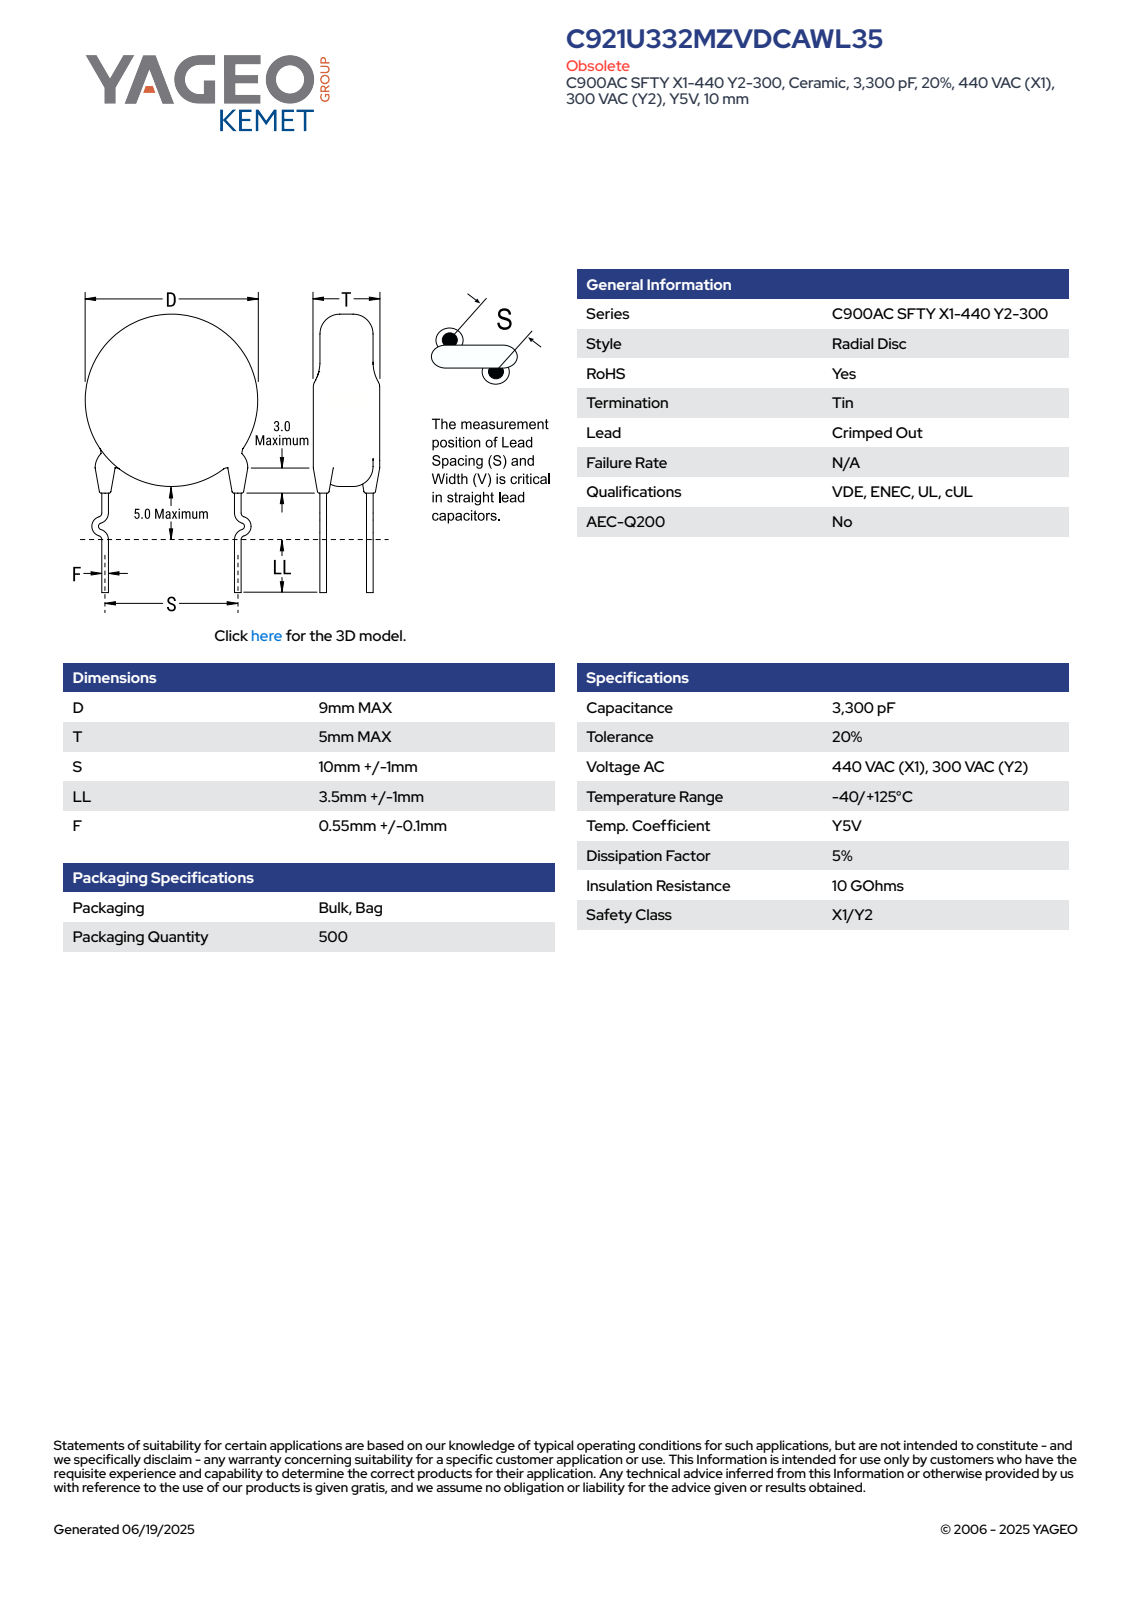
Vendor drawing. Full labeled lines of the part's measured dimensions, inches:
Part name (STEP PRODUCT): CCD_KCOC900_D9T5S10LL4.5F0.55
STEP written by: SolidWorks 2014 (AUTOMOTIVE_DESIGN)
Units: inches
Bodies: 4 solids, 93 faces (63 planar, 10 cylindrical, 20 other)
Overall size (bounding box): 0.728 × 0.571 × 0.23
Volume: 0.02 in³ · Surface area: 0.499 in²
Round bosses / shafts (diameter × count): ⌀0.047 ×2, ⌀0.354 ×1
Partial cylindrical surfaces — rounded edges, fillets, slot ends (radius × count): R0.024 ×2
Main face-to-face distances: 0.197, 0.037, 0.196, 0.159, 0.03, 0.15, 0.023, 0.16, 0.109, 0.113
